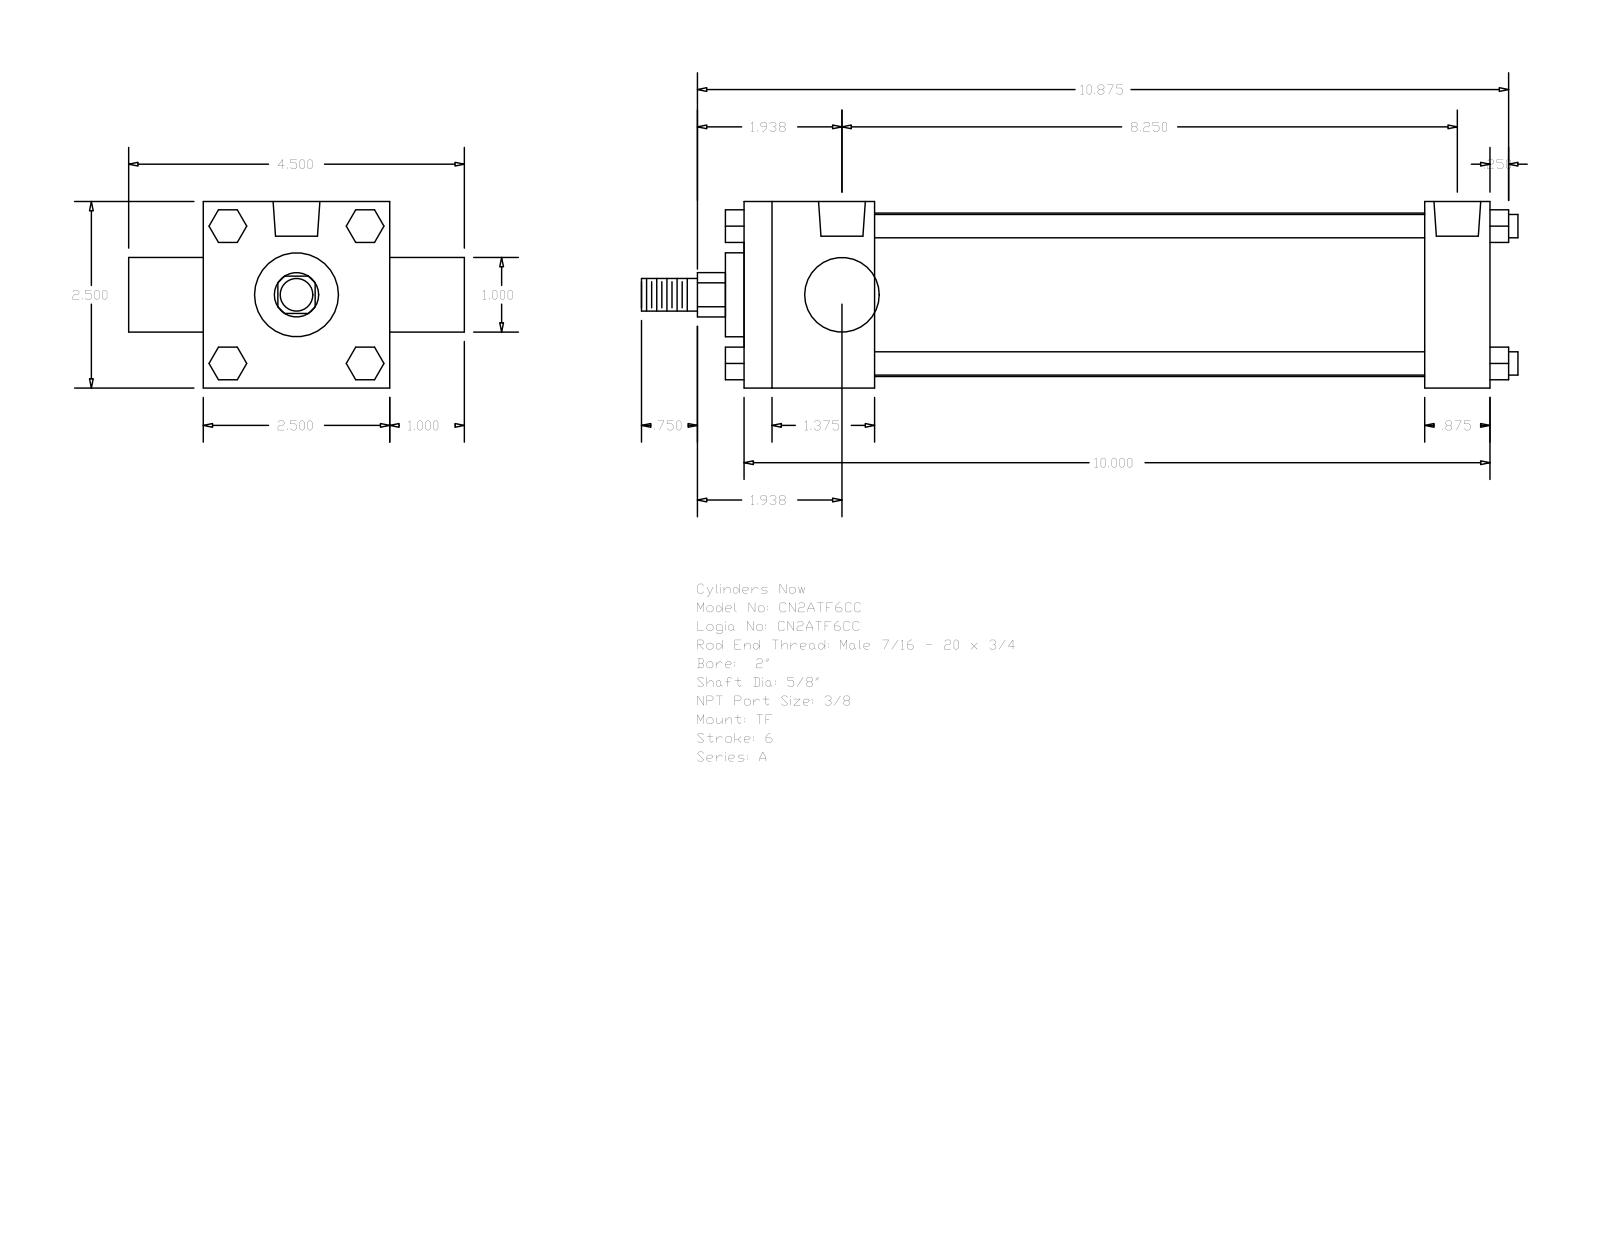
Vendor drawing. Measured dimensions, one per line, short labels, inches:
name: A_TF__0200_0.625
written by: GSSL Pune (CONFIG_CONTROL_DESIGN)
unit: in
bodies: 0 solids, 120 faces (92 planar, 28 cylindrical, 0 other)
size: 11.75 × 4.5 × 2.5
holes: 3× ⌀0.219, 2× ⌀0.627
bosses: 4× ⌀0.313, 1× ⌀2.19, 1× ⌀1.125, 1× ⌀1, 1× ⌀0.625, 1× ⌀0.437
rounds: 1× R0.297
face distances: 2.5, 10, 1.75, 9.125, 7.375, 8.25, 0.875, 1, 3.5, 0.25
hole spacings: 0.156, 0.157, 7.937, 8.093, 8.094, 8.25
